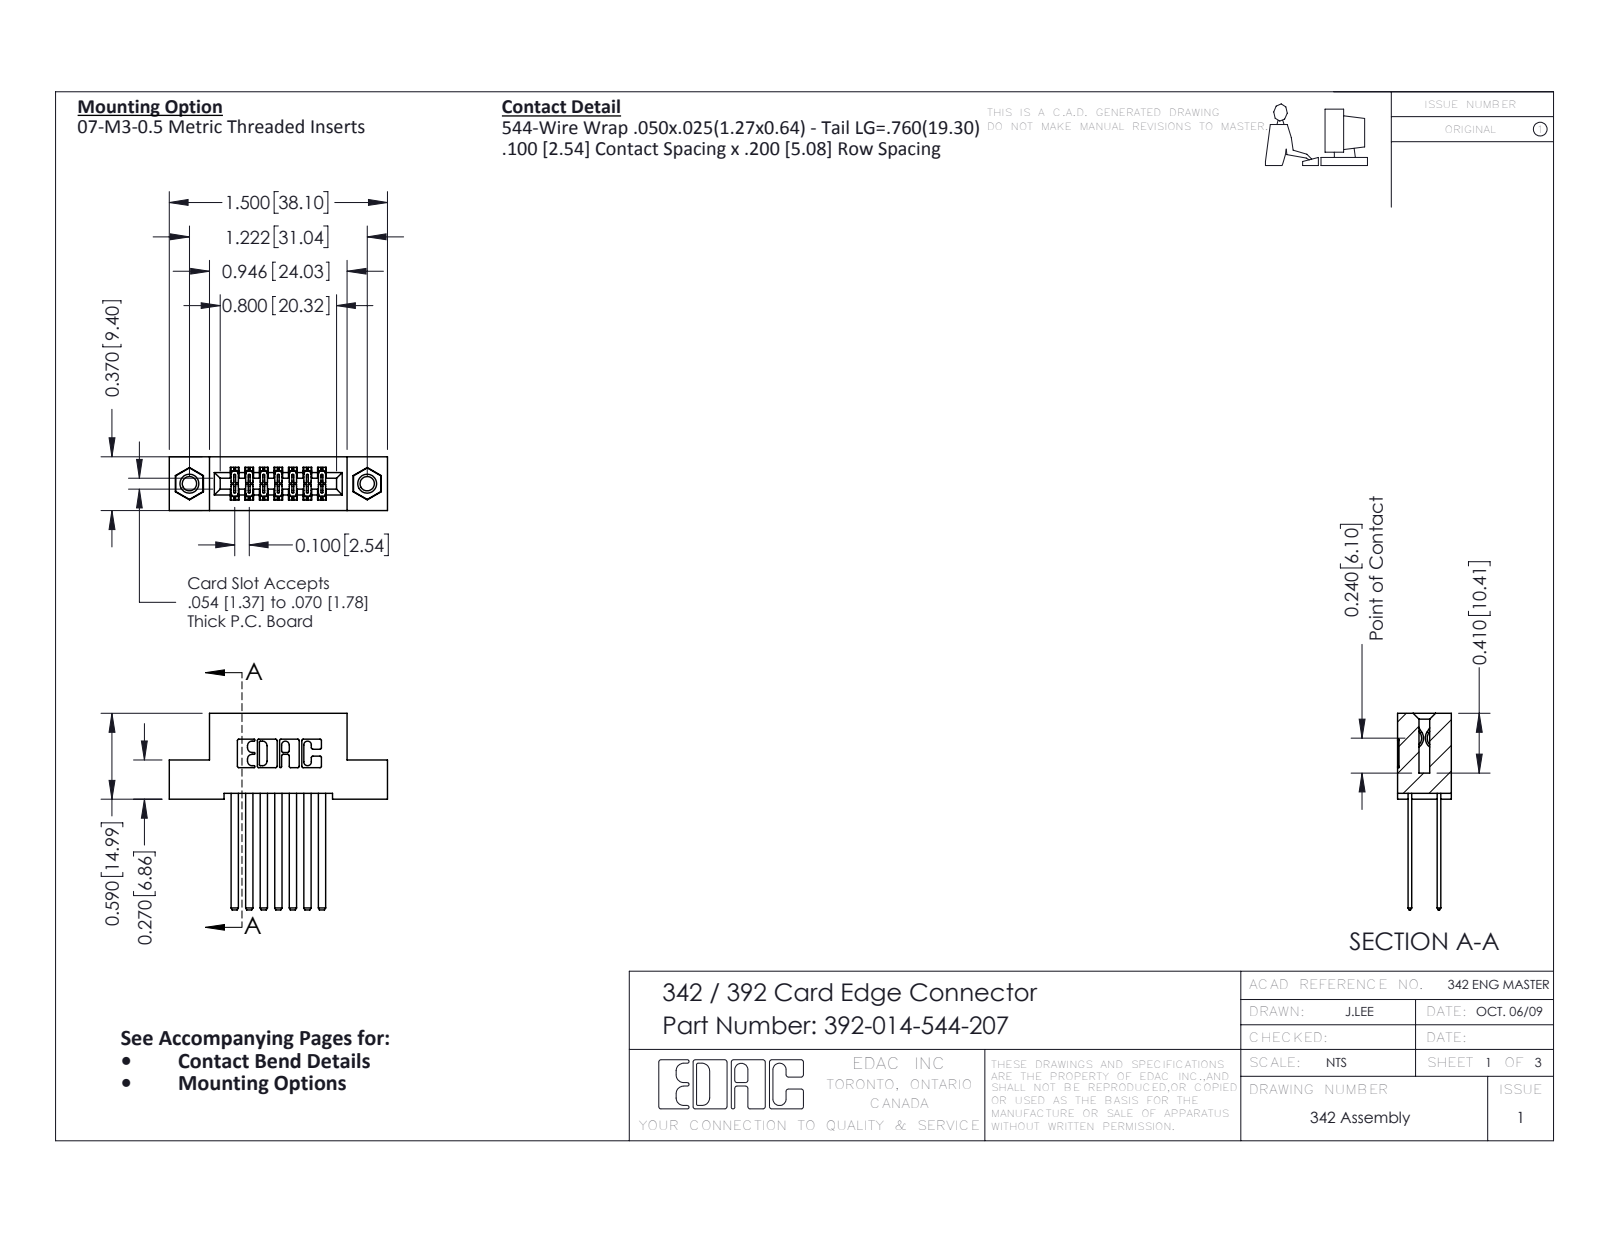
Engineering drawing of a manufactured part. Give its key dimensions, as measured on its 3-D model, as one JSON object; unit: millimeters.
{"part_name": "345-292-001_345-293-144; 345-250-001_345-250-005-103; 392-014-544-207; 342 Part_TI", "step_written_by": "SolidWorks 2016 (CONFIG_CONTROL_DESIGN)", "units": "millimeters", "bodies": {"solids": 17, "faces": 814, "planar": 546, "cylindrical": 252, "other": 16}, "overall_size": [38.1, 34.3, 9.4], "volume_mm3": 3440, "surface_area_mm2": 5308, "round_holes": [[2.5, 2], [3.2, 2], [4, 2]], "round_bosses_or_shafts": [[3.9, 2]], "partial_cylinders_radius": [[0.3, 22], [0.2, 21], [0.2, 6], [0.8, 6], [0.7, 3], [0.4, 2], [0.6, 2], [0.6, 2]], "face_to_face_distances": [5.1, 1.8, 7.6, 2.5, 2.5, 6.9, 0.6, 1, 9.4, 5.7], "hole_center_spacings": [31]}
